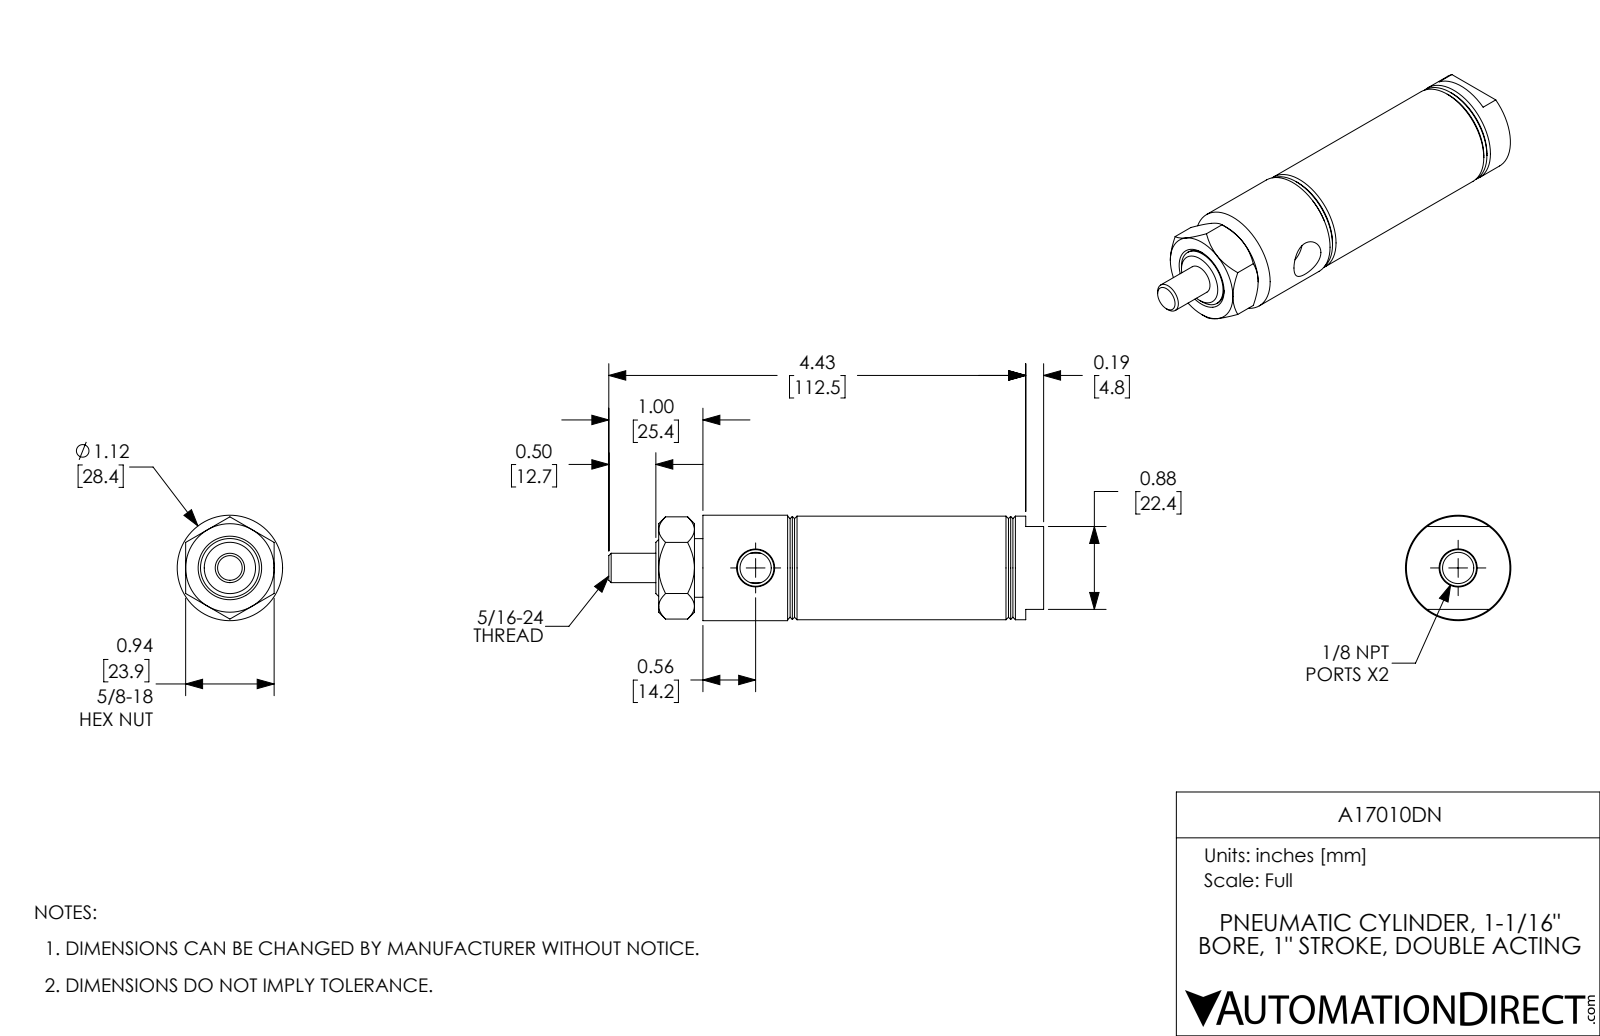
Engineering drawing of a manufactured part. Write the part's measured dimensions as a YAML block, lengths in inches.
part_name: "A17010DN; A17010DN_Mounting Nut_D-9; A17010DN-Rod; A17010DN-MainBody"
step_written_by: "SolidWorks 2017 (AUTOMOTIVE_DESIGN)"
units: inches
bodies: {solids: 3, faces: 94, planar: 24, cylindrical: 26, other: 44}
overall_size: [4.62, 1.12, 1.12]
volume: 2.86
surface_area: 34.29
round_holes:
  - {diameter: 0.332, count: 2}
  - {diameter: 0.312, count: 1}
  - {diameter: 0.625, count: 1}
  - {diameter: 1.063, count: 1}
round_bosses_or_shafts:
  - {diameter: 1.12, count: 1}
  - {diameter: 1.1, count: 1}
  - {diameter: 0.623, count: 1}
face_to_face_distances: [0.5, 1, 2.56, 1.5, 2.06, 1.06, 1.56, 2.56, 3.62, 1.06]
